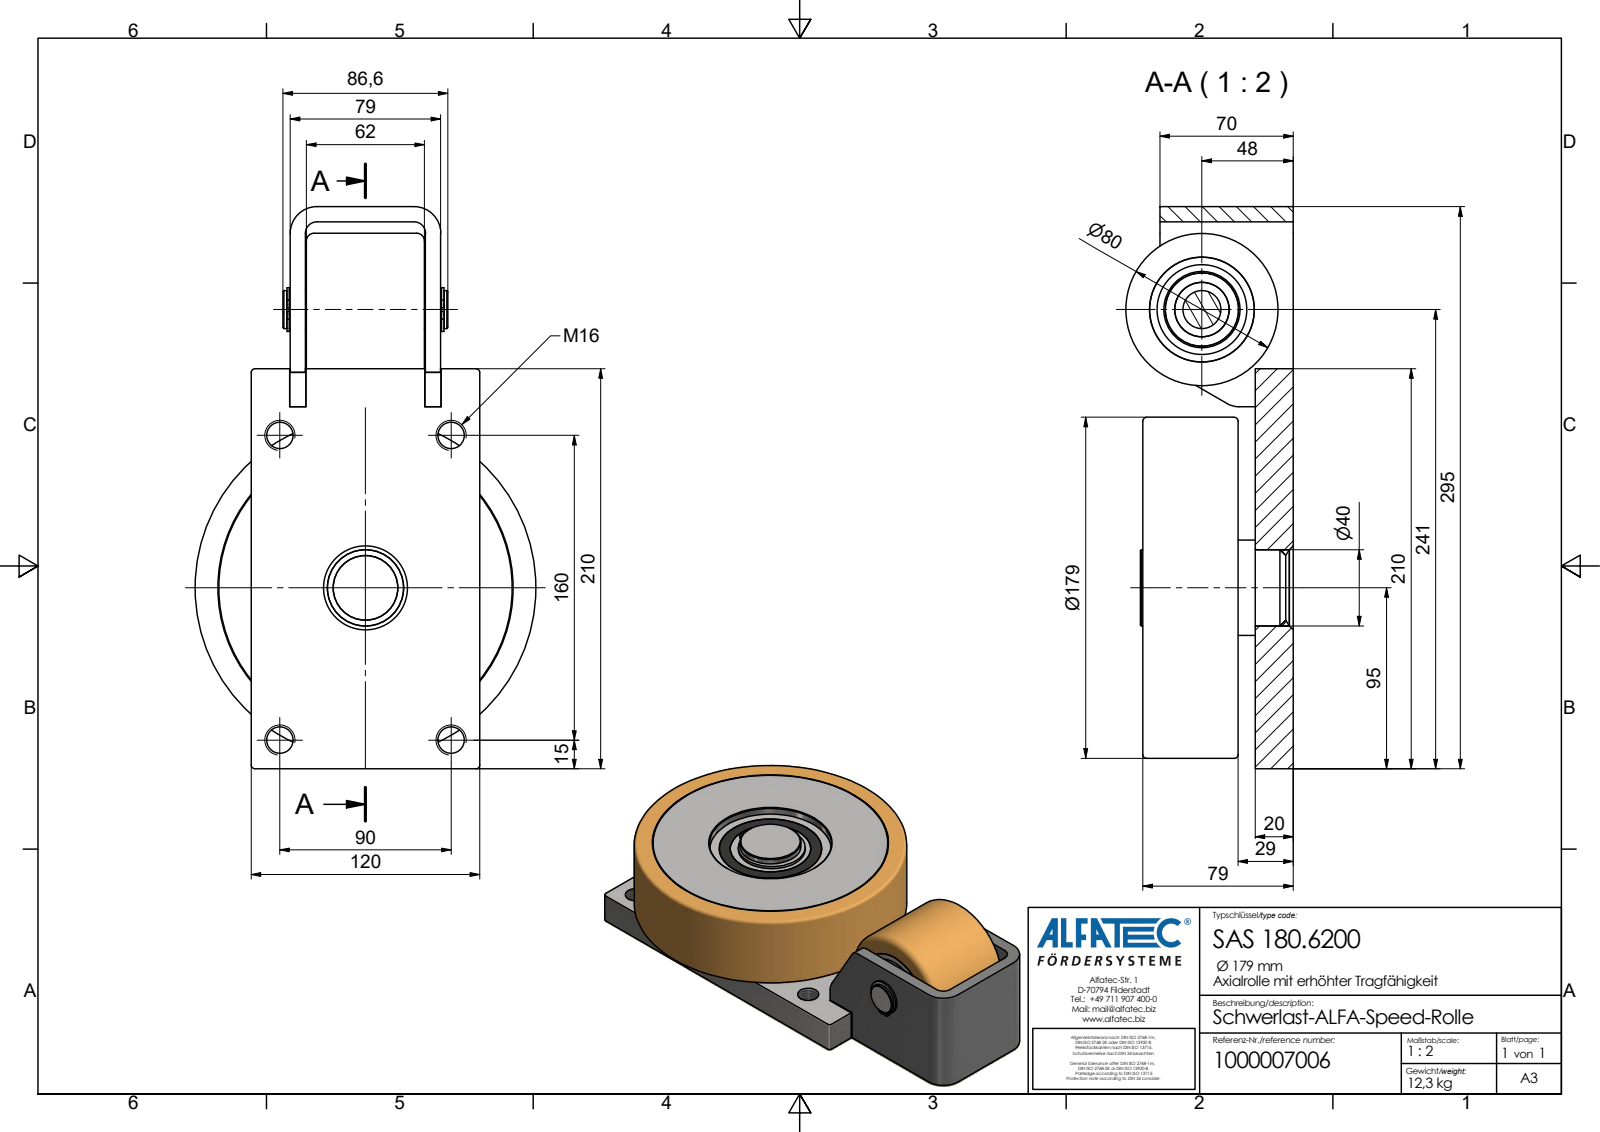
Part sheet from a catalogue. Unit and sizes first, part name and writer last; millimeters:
Units: millimetres
Overall size (bounding box): 295 × 179 × 88
Round holes (diameter × count): ⌀13.84 ×4, ⌀2 ×2
Round bosses / shafts (diameter × count): ⌀20 ×2, ⌀19 ×2, ⌀179 ×1, ⌀80 ×1, ⌀50 ×1, ⌀40 ×1, ⌀22.93 ×1
Partial cylindrical surfaces — rounded edges, fillets, slot ends (radius × count): R2 ×4, R6 ×3, R3 ×2, R14 ×2, R12 ×1
Main face-to-face distances: 29, 79, 50, 9.01, 19.99, 59.01, 8, 71, 20.5, 28.5
Hole centre spacings: 90, 160, 183.58, 5.2
Volume: 2 211 000 mm³ · Surface area: 203 255 mm²
Bodies: 1 solid, 94 faces (47 planar, 38 cylindrical, 9 other)
Part name (STEP PRODUCT): SAS 180.6200_Kontur
STEP written by: Autodesk Inventor 2020 (AP242_MANAGED_MODEL_BASED_3D_ENGINEERING_MIM_LF)
